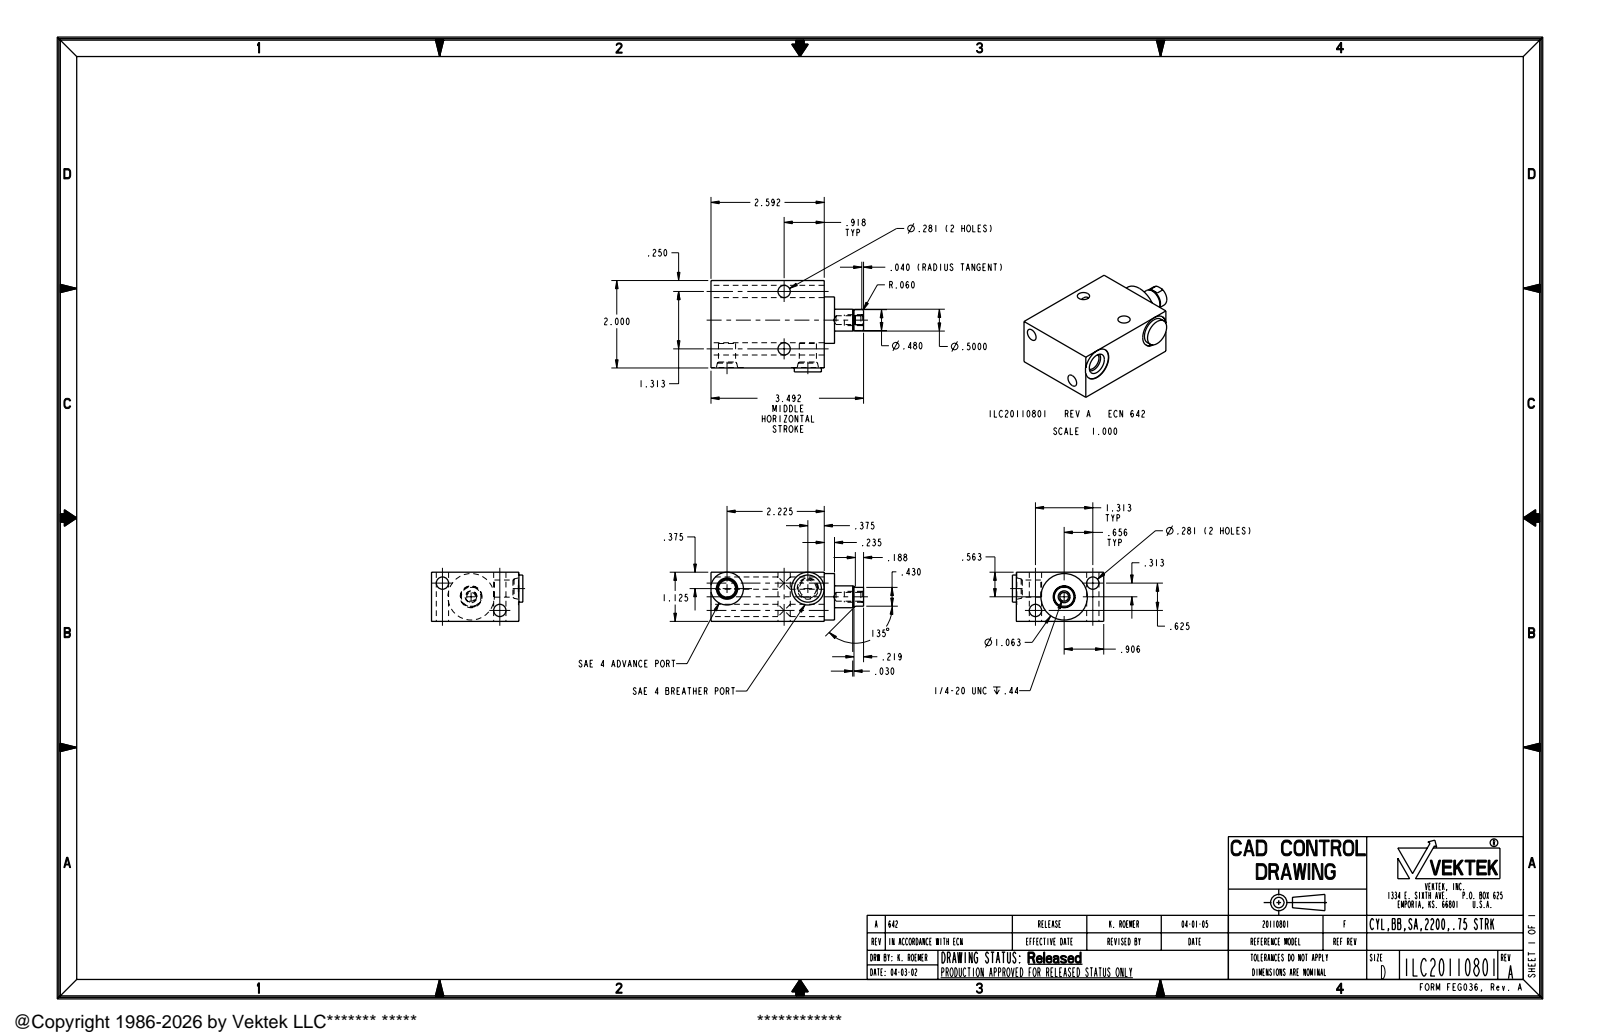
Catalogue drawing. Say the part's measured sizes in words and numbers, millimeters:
The part is named "ILC20110801". Its 3-D file was written by "PRO/ENGINEER BY PARAMETRIC TECHNOLOGY CORPORATION, 2004290 (AUTOMOTIVE_DESIGN_CC2)". It is 1 solid with 72 faces: 21 planar, 35 cylindrical and 16 other. Overall it measures 88.7 by 53.1 by 28.6 millimeters. Its volume is 91 620 cubic millimeters and its surface area 19 720 square millimeters. Round holes: 4 of diameter 7.1, 2 of diameter 10, 2 of diameter 19.1, 1 of diameter 5.1. Round bosses or shafts: 1 of diameter 27, 1 of diameter 15.7, 1 of diameter 12.7, 1 of diameter 12.2, 1 of diameter 6.4. The main face-to-face distances are 28.6, 50.8, 65.8, 6, 71.8, 50.5, 2.3, 2.5, 53.1, 16.5. The hole center spacings are 18.5, 18.5, 33.4, 36.9, 47.
